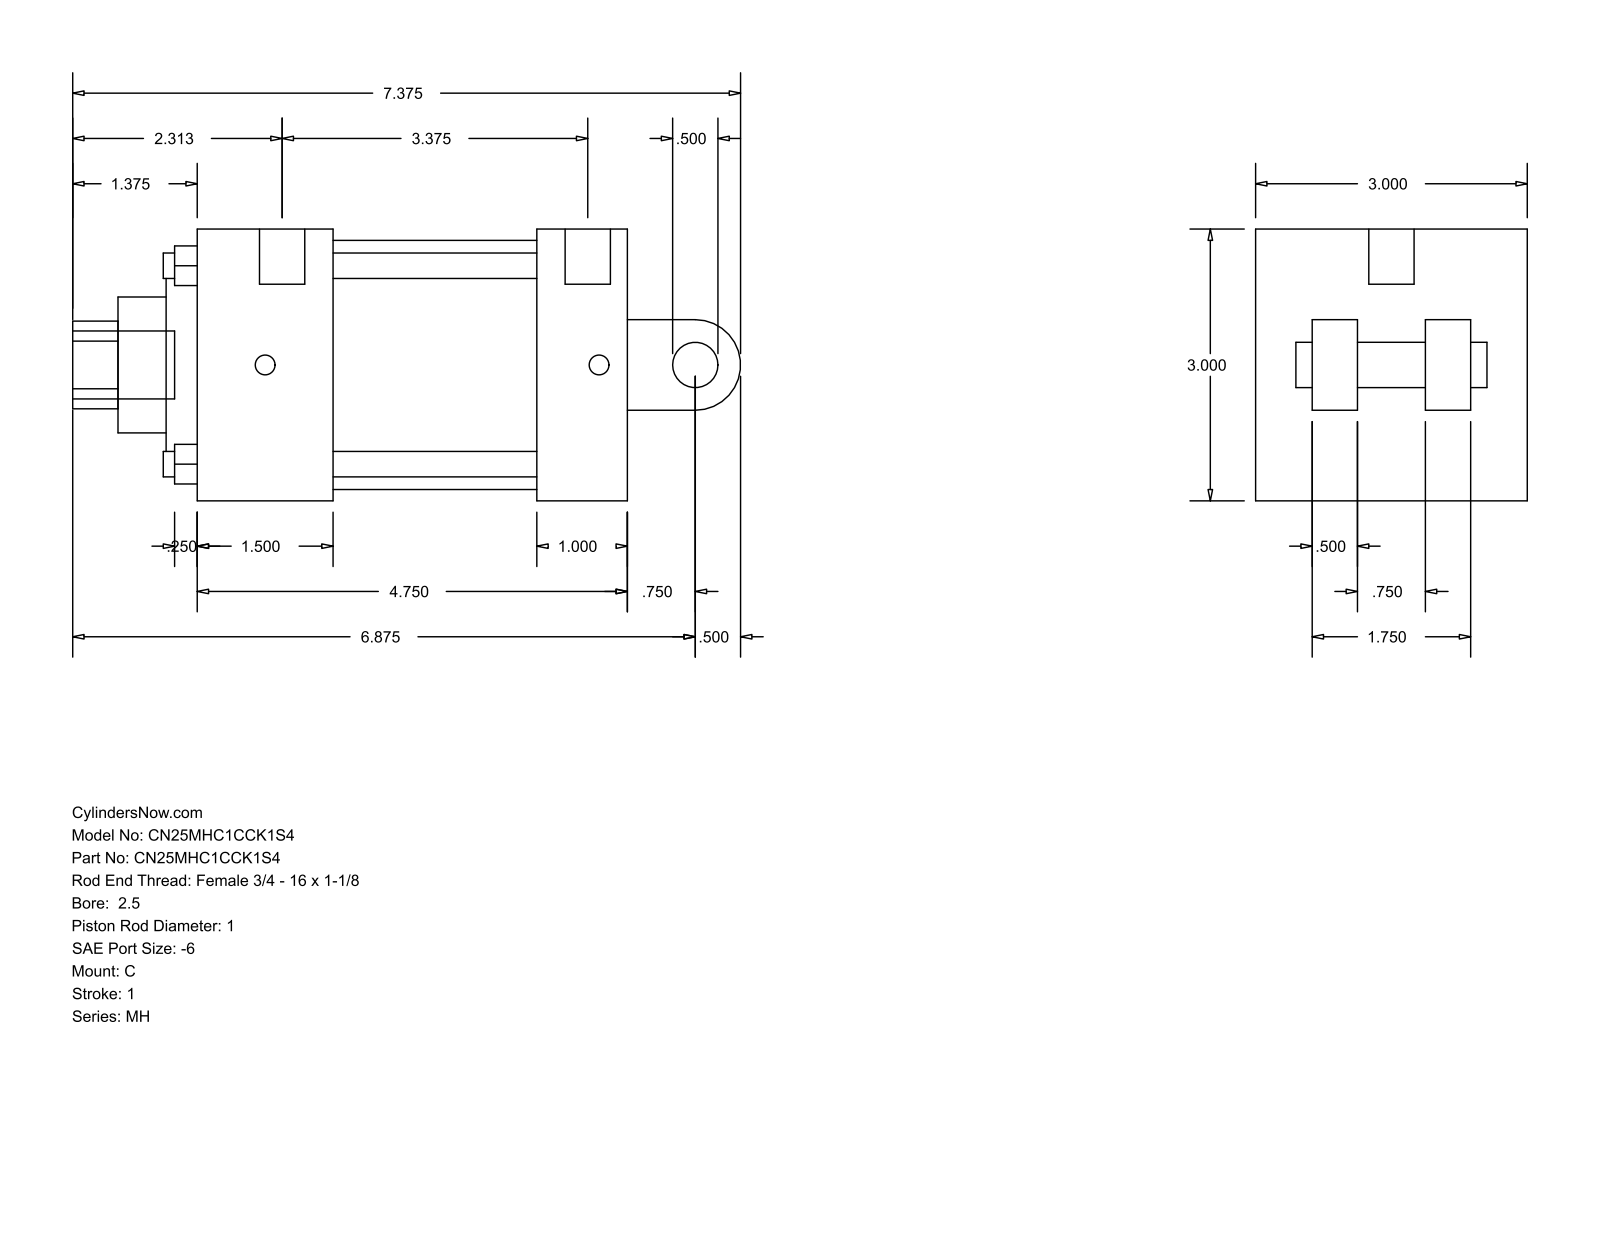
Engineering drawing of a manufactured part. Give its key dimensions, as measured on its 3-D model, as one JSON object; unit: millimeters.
{"part_name": "MH_C__0250_1", "step_written_by": "GSSL Pune (CONFIG_CONTROL_DESIGN)", "units": "millimeters", "bodies": {"solids": 0, "faces": 101, "planar": 71, "cylindrical": 30, "other": 0}, "overall_size": [187.32, 76.2, 76.2], "round_holes": [[7.14, 4], [5.56, 2], [12.7, 1], [25.4, 1], [38.1, 1], [60.33, 1], [69.85, 1]], "round_bosses_or_shafts": [[12.7, 2], [5.56, 2], [19.05, 1]], "partial_cylinders_radius": [[12.29, 1], [12.7, 1]], "face_to_face_distances": [76.2, 120.65, 15.87, 25.39, 60.33, 95.26, 38.11, 57.15, 82.54, 12.7], "hole_center_spacings": [39.33, 55.62, 78.66, 3.18]}
